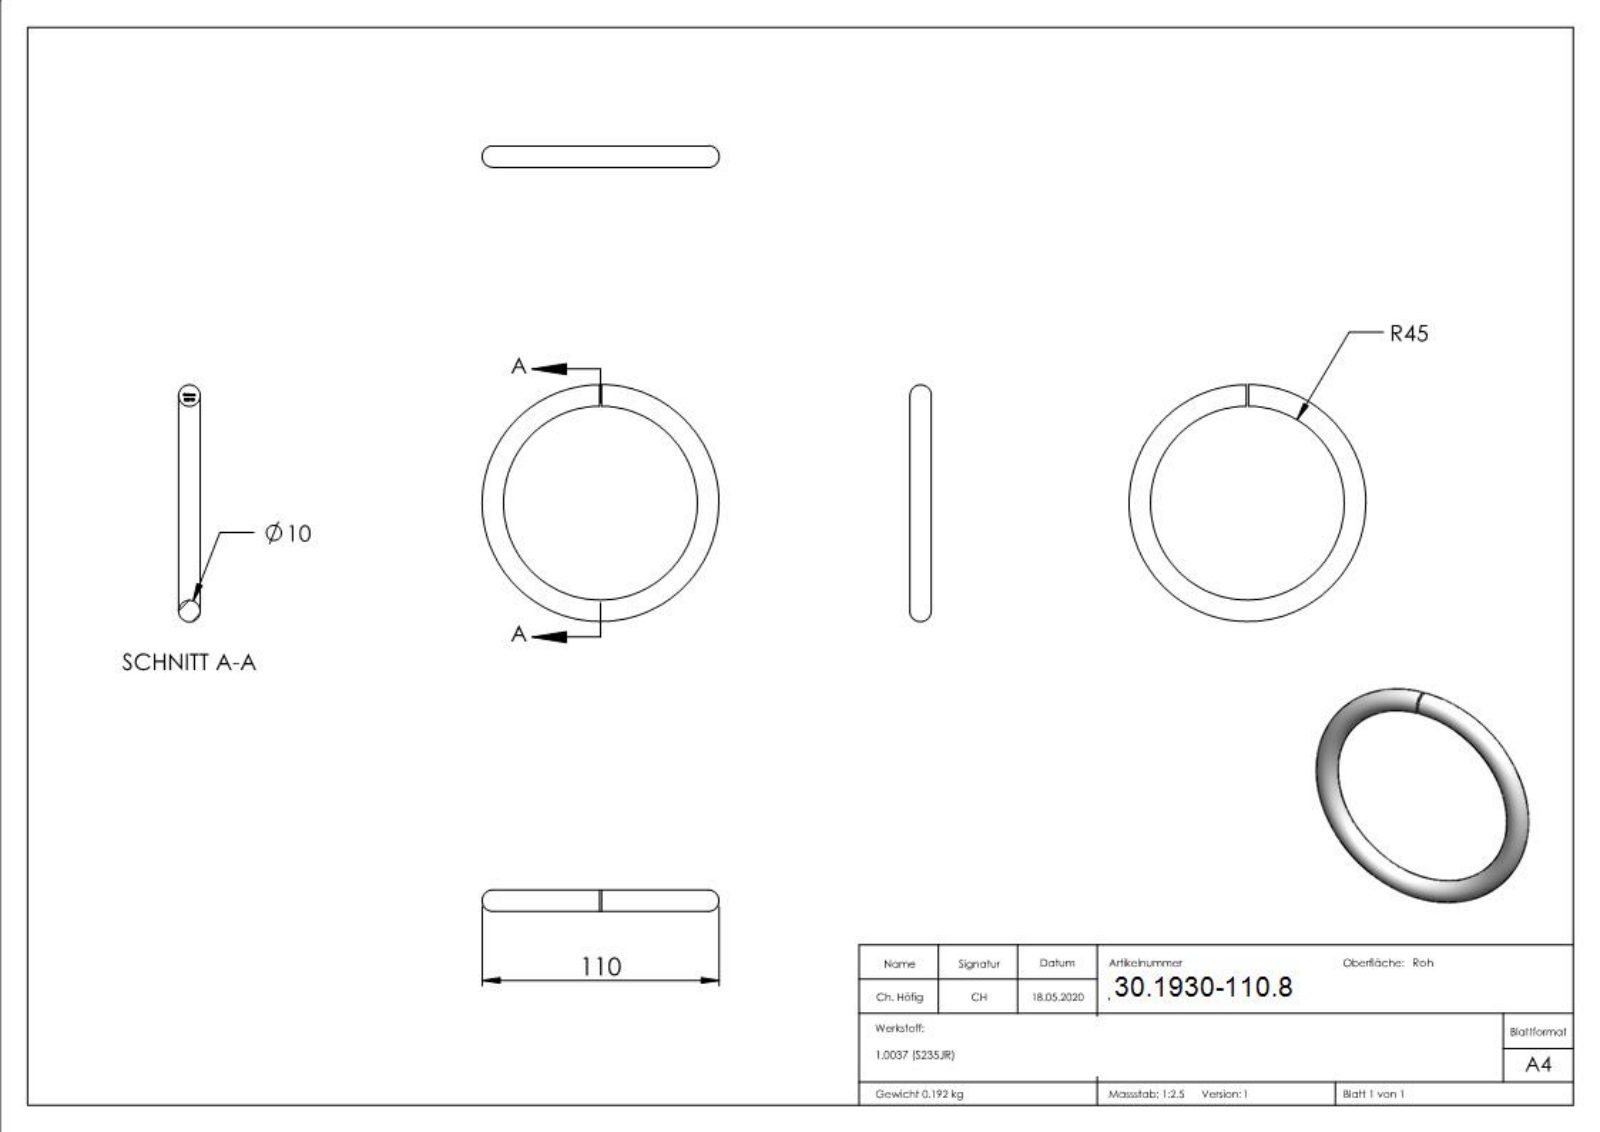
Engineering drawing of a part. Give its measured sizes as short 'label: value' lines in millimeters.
name: 5629-110
written by: SolidWorks 2015 (CONFIG_CONTROL_DESIGN)
unit: mm
bodies: 1 solid, 211 faces (108 planar, 0 cylindrical, 103 other)
size: 110 × 110 × 10
volume: 24 589 mm³; area: 10 022 mm²
face distances: 1, 1.5, 0.5, 1.78, 0.83, 2.45, 2.12, 0.99, 0.61, 2.73
